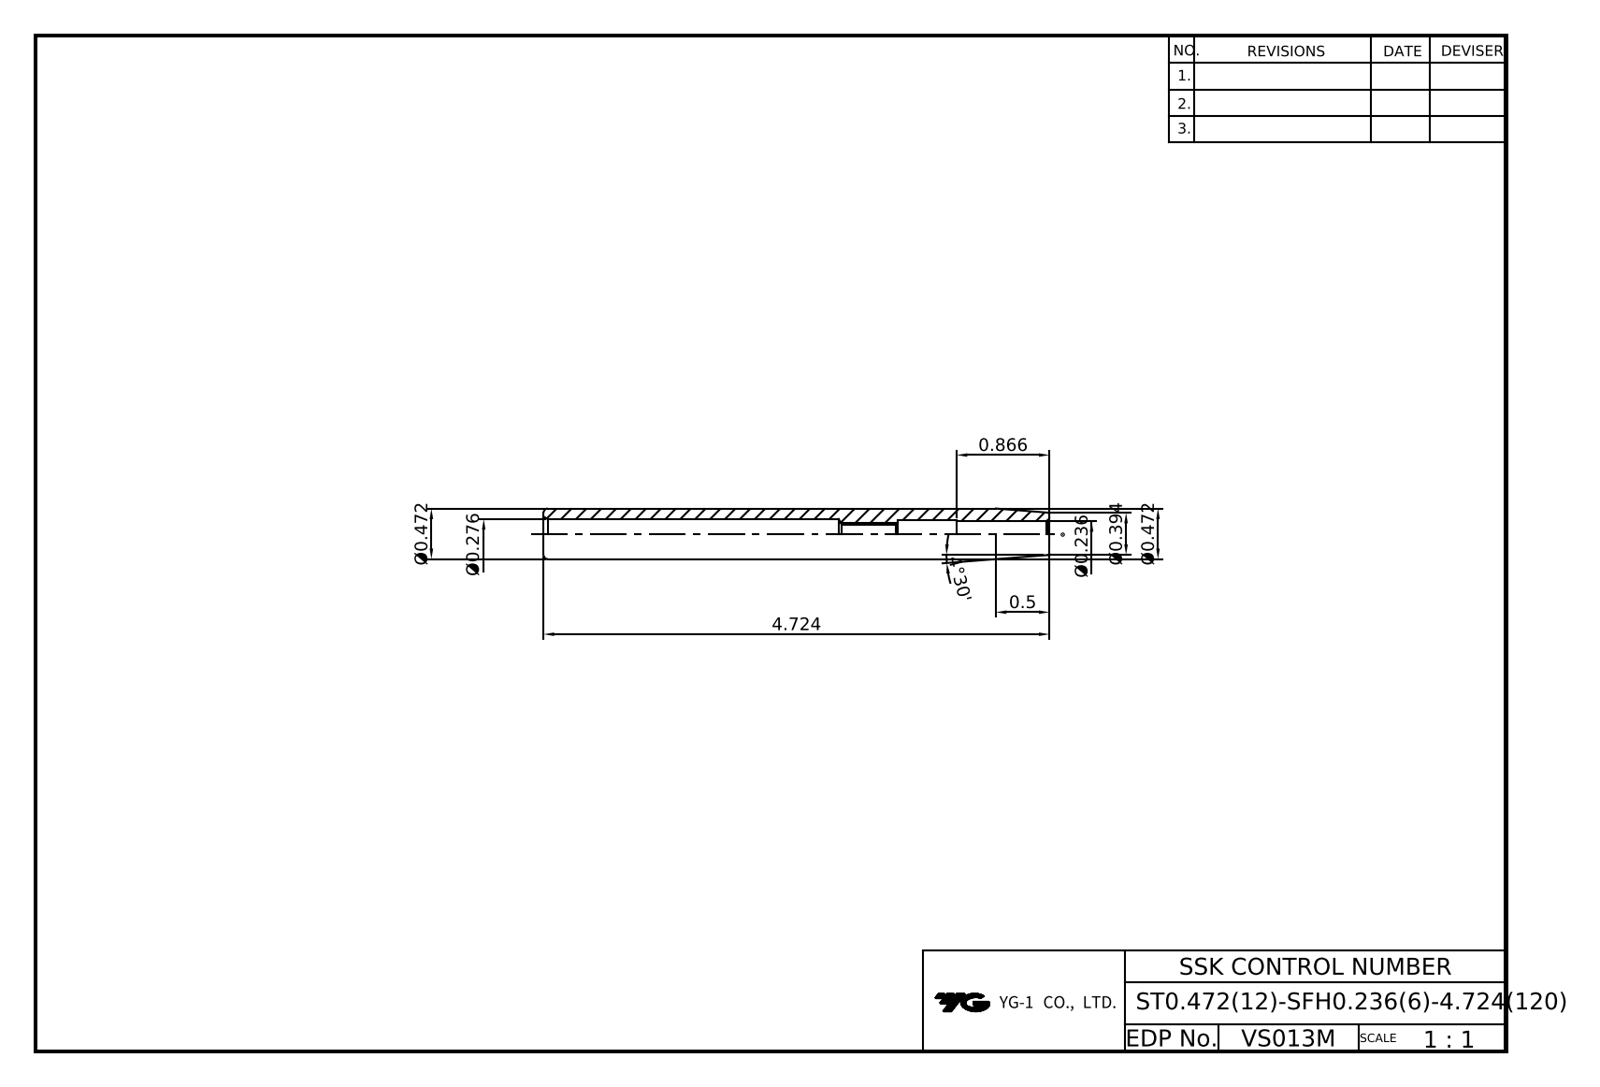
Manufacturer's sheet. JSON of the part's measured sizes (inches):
{"part_name": "LO-ST12-SFH6-120", "step_written_by": "Autodesk Inventor 2022 (AUTOMOTIVE_DESIGN)", "units": "inches", "bodies": {"solids": 1, "faces": 13, "planar": 4, "cylindrical": 5, "other": 4}, "overall_size": [4.724, 0.472, 0.472], "volume_in3": 0.566, "surface_area_in2": 10.99, "round_holes": [[0.169, 1], [0.236, 1], [0.276, 1]], "round_bosses_or_shafts": [[0.472, 1]], "face_to_face_distances": [4.724, 3.307, 1.417, 3.858, 0.551, 0.866]}
